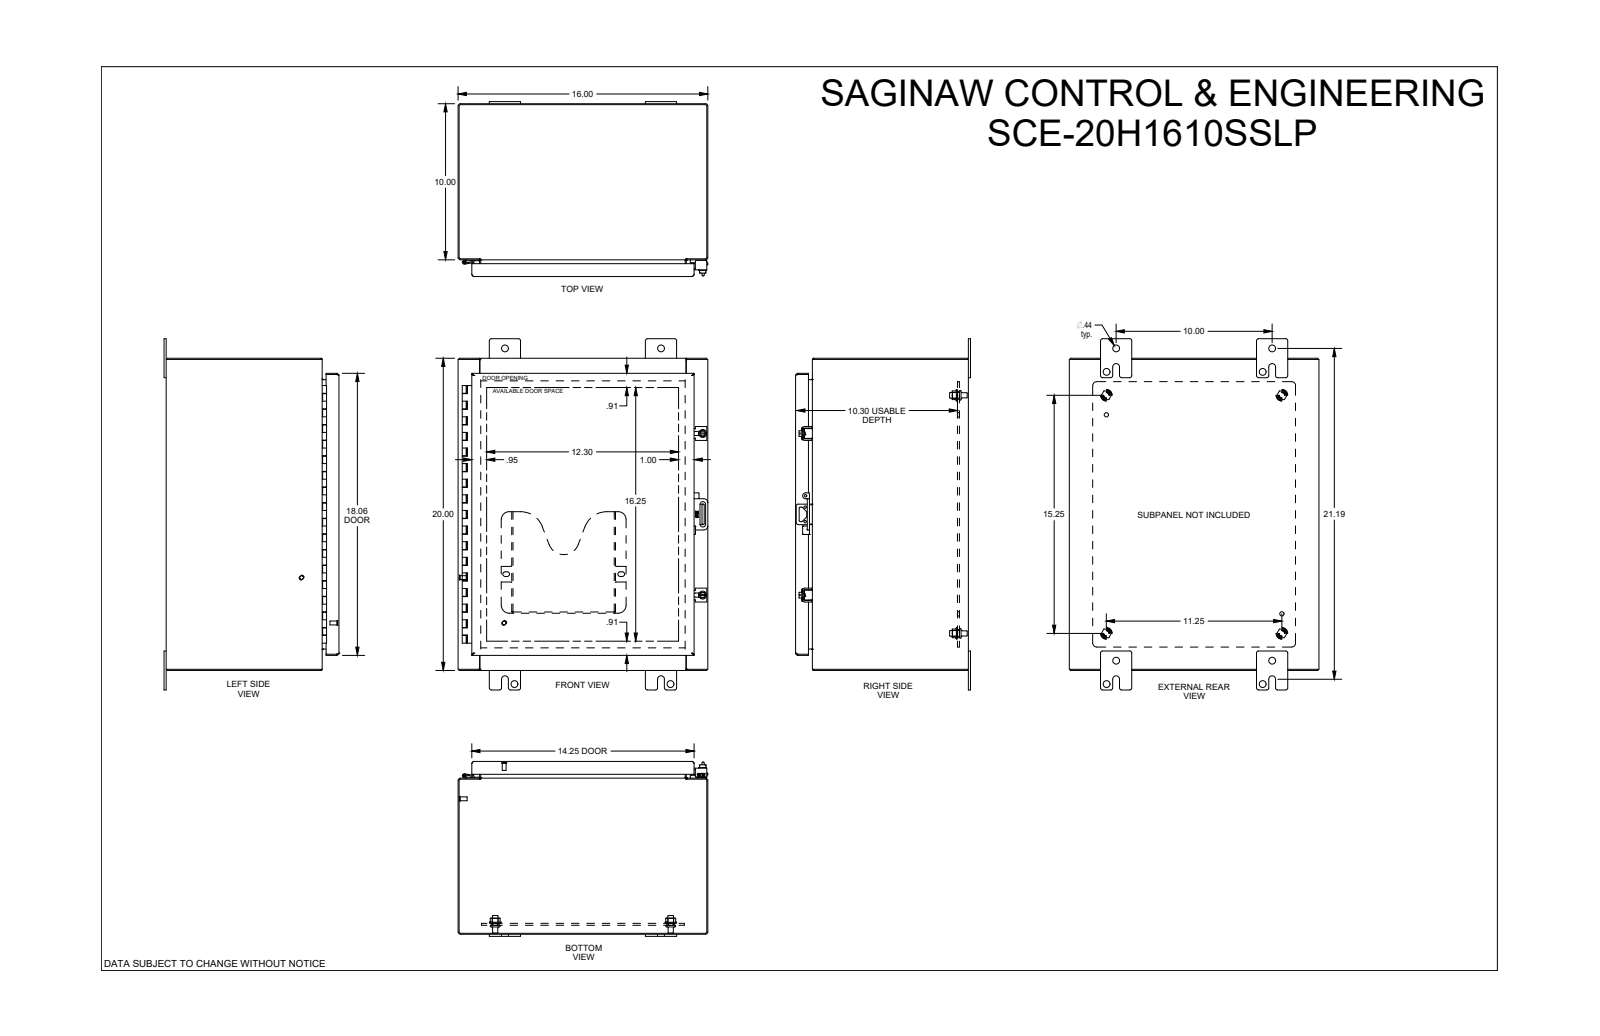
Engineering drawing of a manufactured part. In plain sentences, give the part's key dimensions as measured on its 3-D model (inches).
The part is named "SCE-20H1610SSLP". Its 3-D file was written by "SolidWorks 2019 (CONFIG_CONTROL_DESIGN)". It is 0 solids with 3015 faces: 1210 planar, 622 cylindrical and 1183 other. Overall it measures 22.5 by 16 by 11.208 inches. Round holes: 8 of diameter 0.437, 5 of diameter 0.25, 4 of diameter 0.367, 4 of diameter 0.5, 3 of diameter 0.19, 3 of diameter 0.193, 2 of diameter 0.16, 2 of diameter 0.203, 2 of diameter 0.281, 1 of diameter 0.13, 1 of diameter 0.132. Round bosses or shafts: 7 of diameter 0.248, 5 of diameter 0.563, 4 of diameter 0.366, 4 of diameter 0.332, 3 of diameter 0.256, 3 of diameter 0.25, 3 of diameter 0.188, 2 of diameter 0.507. Partial cylindrical surfaces (rounded edges, fillets, slot ends): 108 of radius 0.01, 36 of radius 0.015, 30 of radius 0.029, 27 of radius 0.03, 27 of radius 0.125, 25 of radius 0.06, 22 of radius 0.04, 14 of radius 0.07. The main face-to-face distances are 0.075, 15.925, 19.925, 10.998, 10.923, 0.075, 11.073, 10.998, 0.5, 0.625. The hole center spacings are 10, 3.065, 11.041, 17.011, 20.047, 0.515, 1.25, 1.439.
